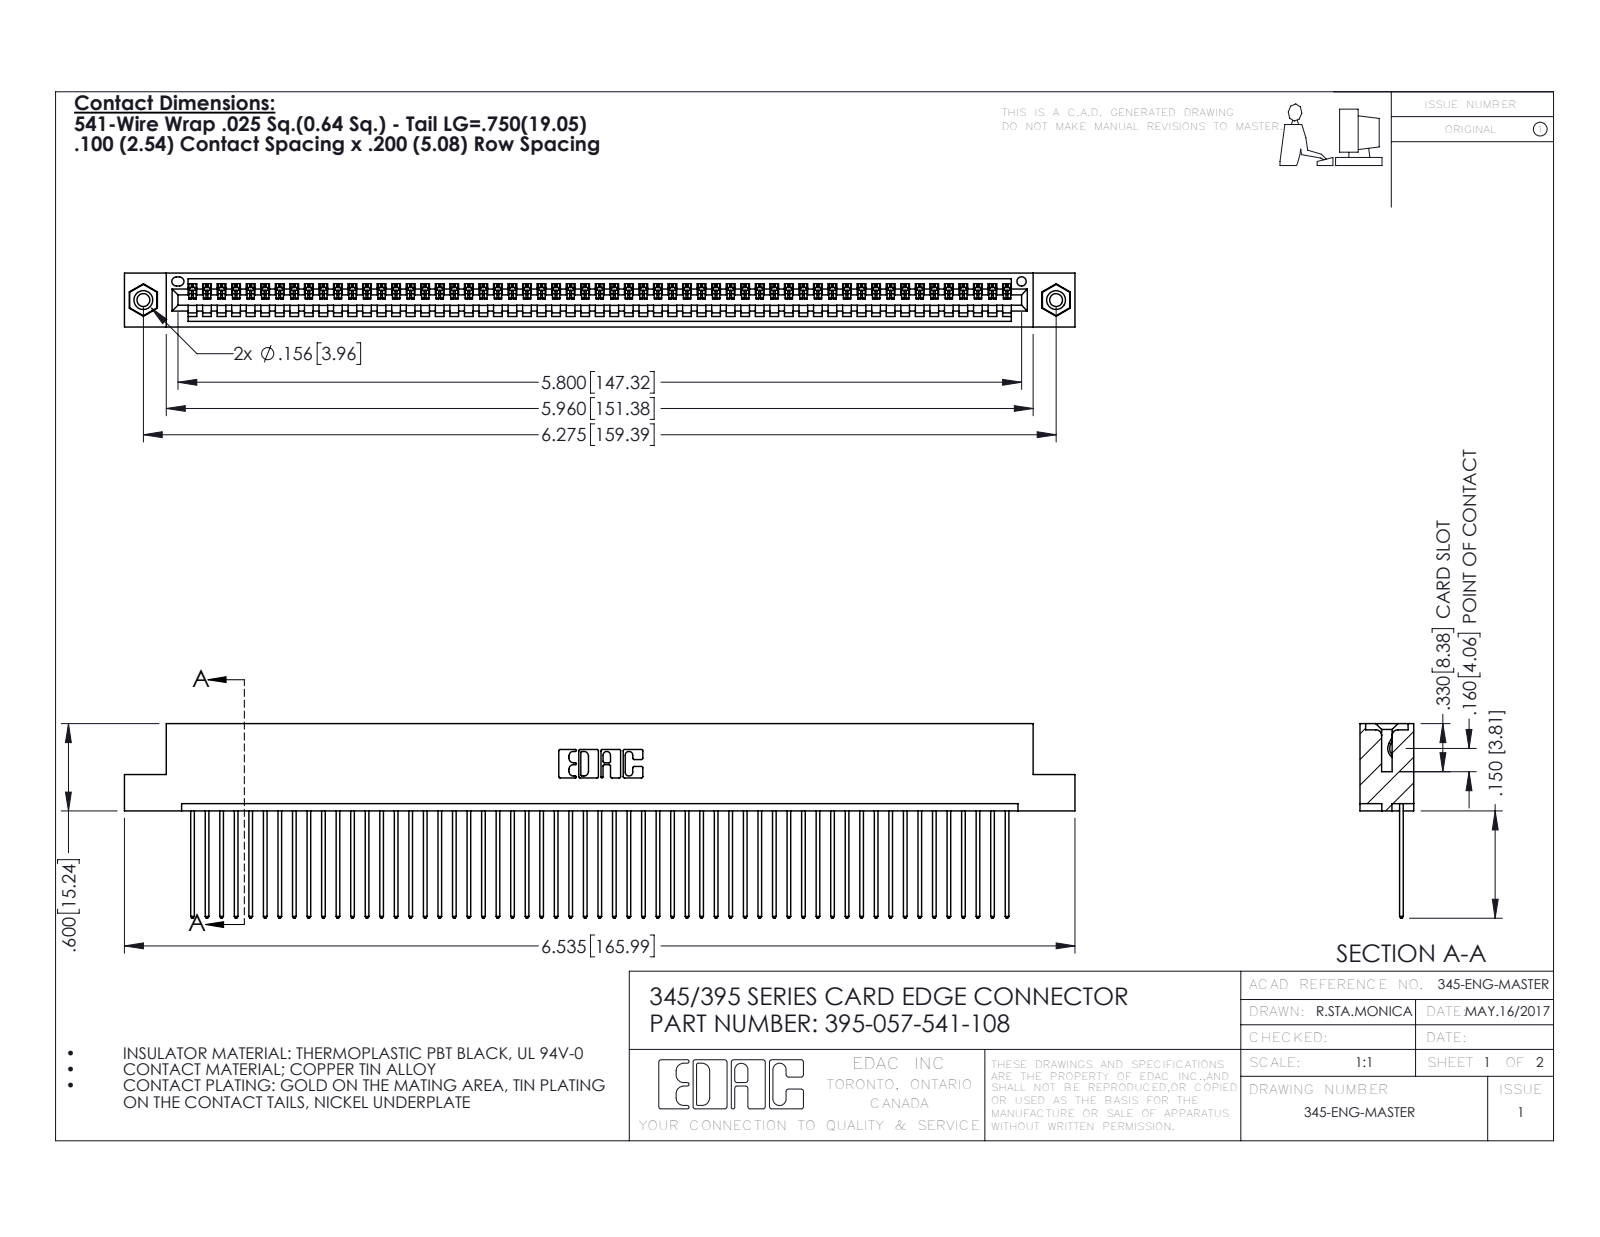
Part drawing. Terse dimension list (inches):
name: 345-250-001_345-250-003-102; 395-057-541-108; 345-292-001_345-293-141; 345 Part_Flush Mounting Lugs - 0.156 Dia-TI
written by: SolidWorks 2016 (CONFIG_CONTROL_DESIGN)
unit: in
bodies: 60 solids, 3492 faces (2392 planar, 1084 cylindrical, 16 other)
size: 6.535 × 1.337 × 0.37
volume: 0.981 in³; area: 35.16 in²
holes: 2× ⌀0.089, 2× ⌀0.125, 2× ⌀0.156, 1× ⌀0.064
bosses: 2× ⌀0.155
rounds: 114× R0.006, 114× R0.01, 22× R0.01, 6× R0.007, 6× R0.031, 3× R0.026, 2× R0.031, 2× R0.04
face distances: 0.072, 0.298, 0.098, 0.272, 0.025, 0.37, 0.2, 0.225, 0.149, 0.072
hole spacings: 0.27, 6.039, 6.275
